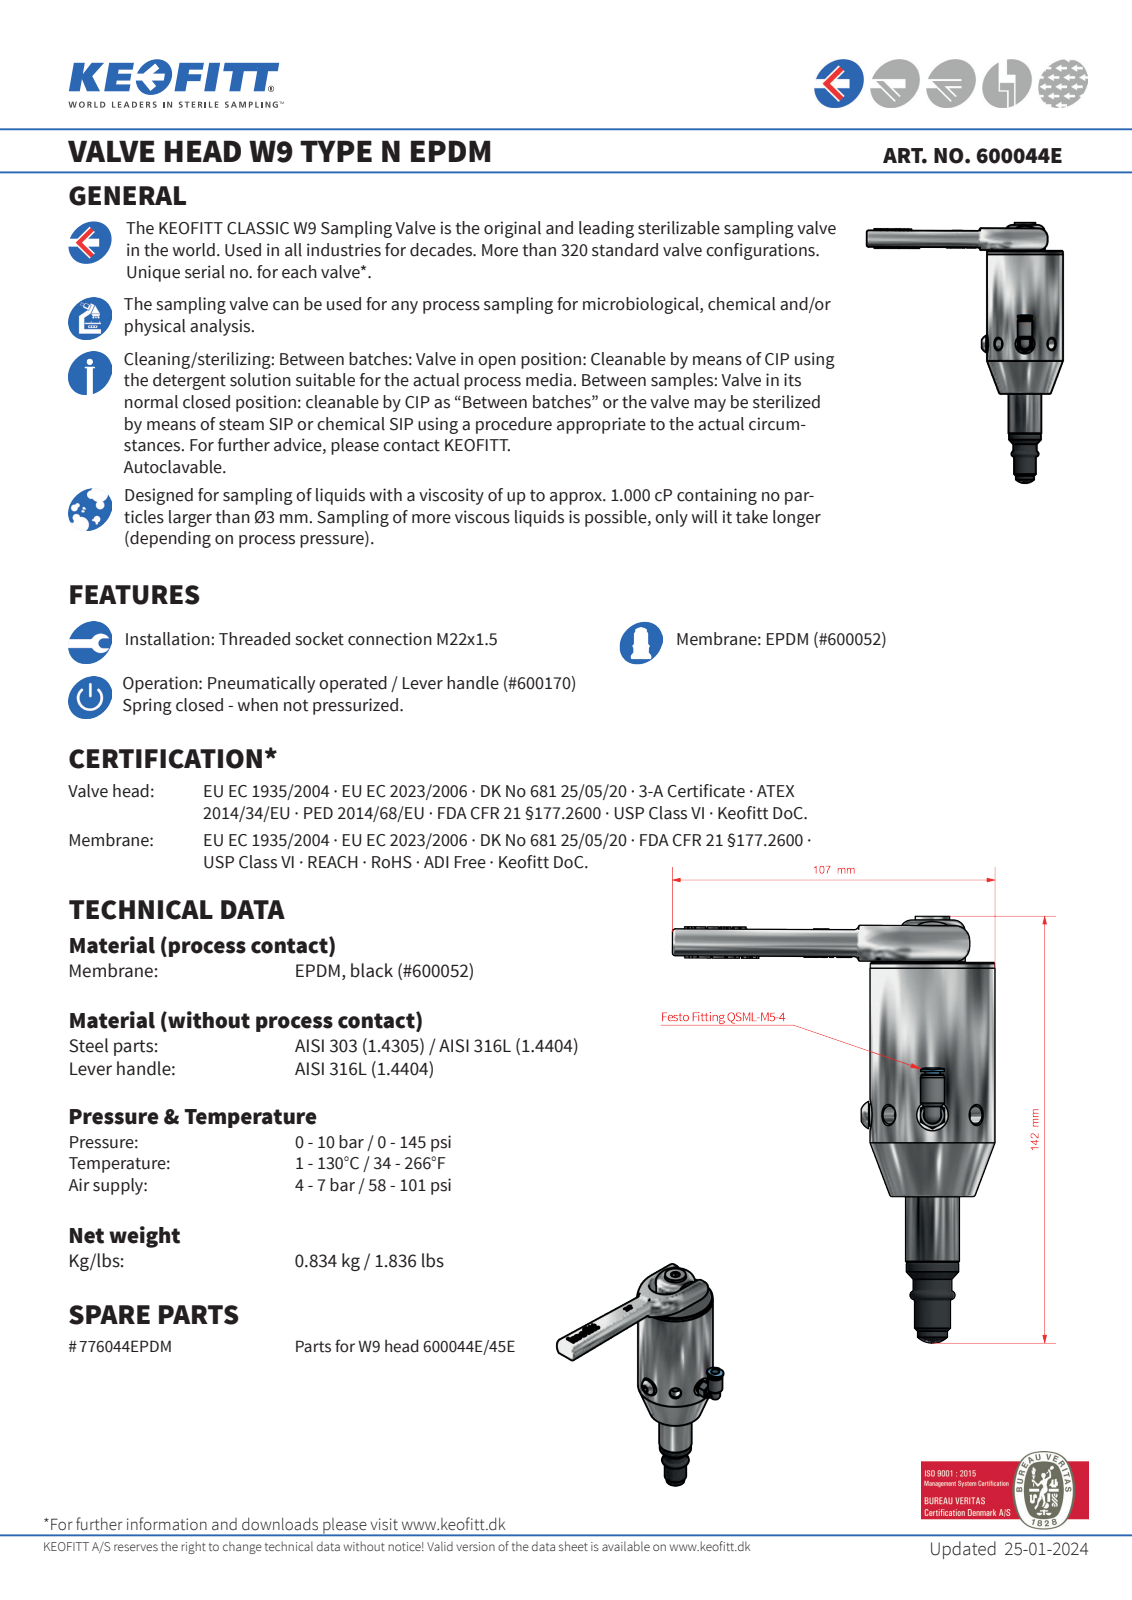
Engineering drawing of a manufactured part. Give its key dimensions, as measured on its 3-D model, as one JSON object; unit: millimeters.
{"part_name": "600044E_test asm simplify", "step_written_by": "Autodesk Inventor 2022 (AUTOMOTIVE_DESIGN)", "units": "millimeters", "bodies": {"solids": 2, "faces": 526, "planar": 219, "cylindrical": 69, "other": 238}, "overall_size": [194.23, 149.91, 67.1], "volume_mm3": 127046, "surface_area_mm2": 22533, "round_holes": [[4, 1], [6, 1]], "round_bosses_or_shafts": [[7.4, 2], [6.6, 2], [6, 2], [5.6, 2], [41.6, 1], [41.5, 1], [18, 1], [17.5, 1]], "partial_cylinders_radius": [[0.5, 14], [0.2, 10], [1, 2], [1.5, 2], [3.9, 2], [5, 2], [3, 1], [9.1, 1]], "face_to_face_distances": [10.5, 1.5, 9, 88.7, 79.7, 78.2, 12, 90.2, 2, 3.1]}
